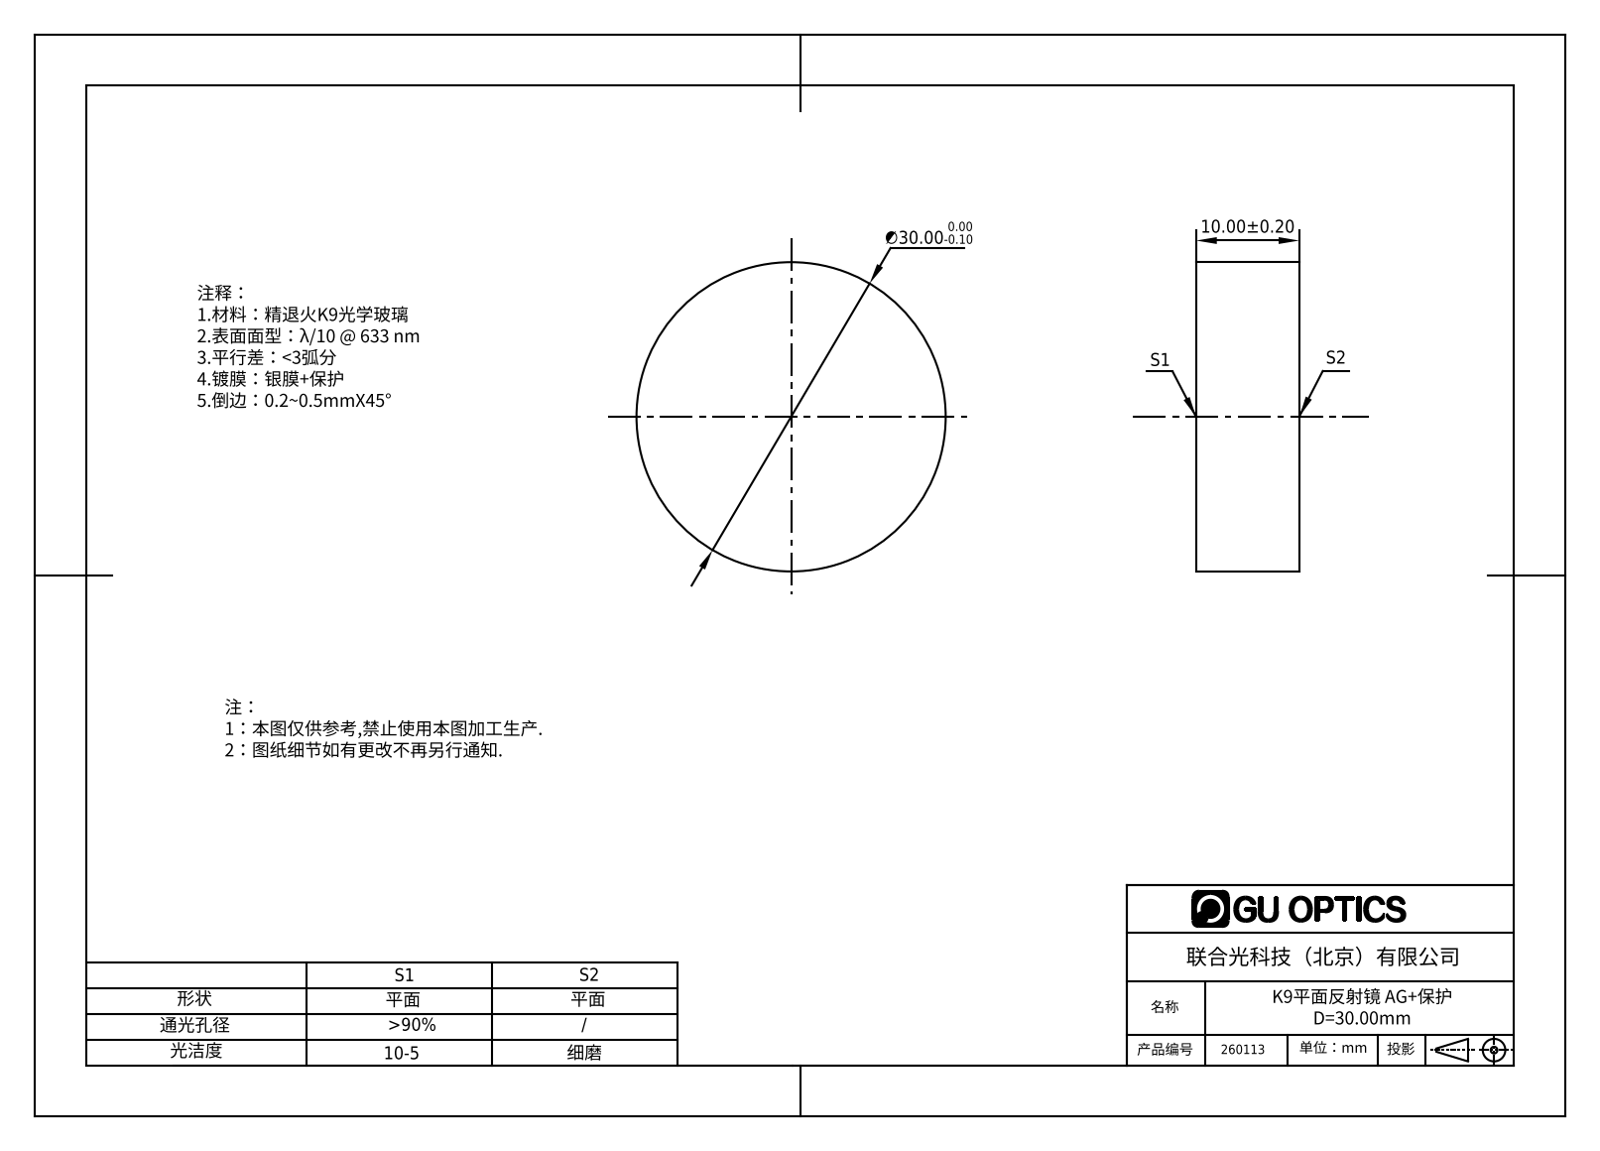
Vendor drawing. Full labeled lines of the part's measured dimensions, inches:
Part name (STEP PRODUCT): 260074
STEP written by: SolidWorks 2016 (AUTOMOTIVE_DESIGN)
Units: inches
Bodies: 1 solid, 4 faces (2 planar, 2 cylindrical, 0 other)
Overall size (bounding box): 1.181 × 1.181 × 0.394
Volume: 0.431 in³ · Surface area: 3.652 in²
Round bosses / shafts (diameter × count): ⌀1.181 ×1
Main face-to-face distances: 0.394
